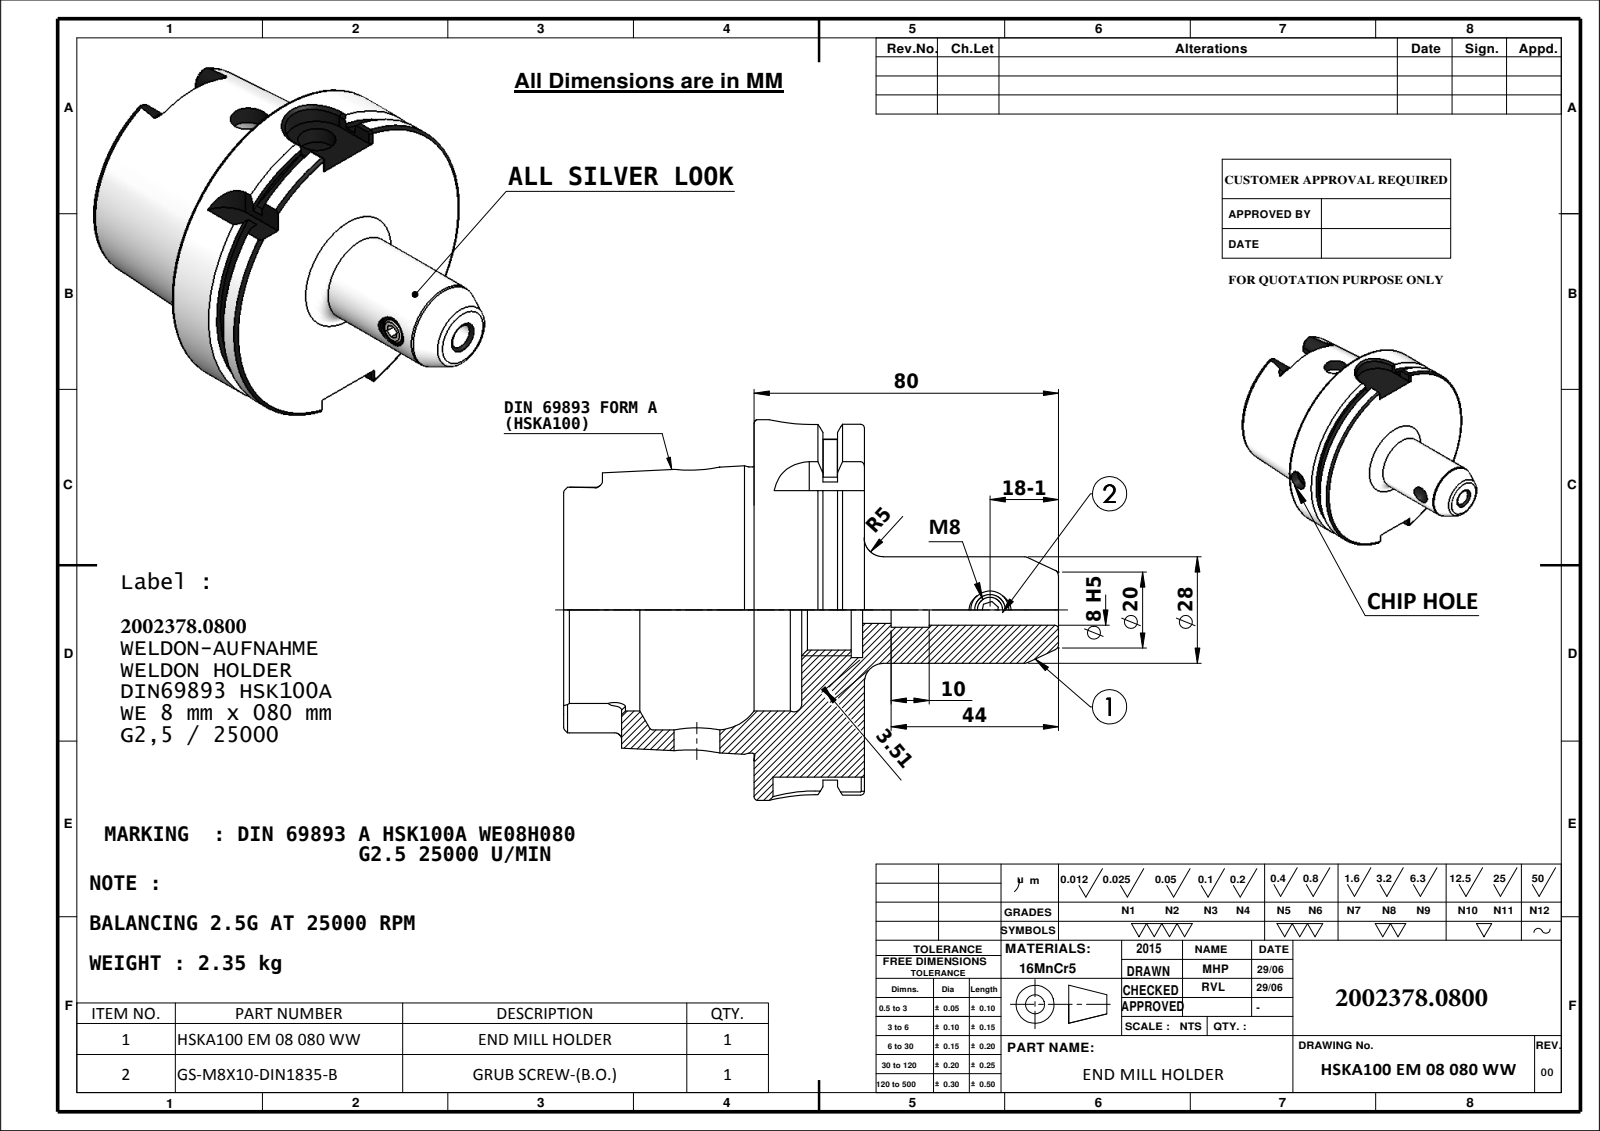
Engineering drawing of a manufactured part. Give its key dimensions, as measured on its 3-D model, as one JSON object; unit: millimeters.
{"part_name": "91100A-WE8 08080; M8X10._DIN 913 - M8 x 8-N; HSKA100 EM 08 080 WW", "step_written_by": "SolidWorks 2009 (CONFIG_CONTROL_DESIGN)", "units": "millimeters", "bodies": {"solids": 2, "faces": 204, "planar": 64, "cylindrical": 58, "other": 82}, "overall_size": [130, 100, 100], "volume_mm3": 281771, "surface_area_mm2": 55679, "round_holes": [[10, 2], [12, 2], [6.8, 1], [7, 1], [8, 1], [9, 1], [21, 1], [25, 1], [53, 1], [63, 1]], "round_bosses_or_shafts": [[100, 1], [92, 1], [75.16, 1], [28, 1], [8, 1]], "partial_cylinders_radius": [[1.8, 6], [4.88, 4], [10, 2], [11, 1]], "face_to_face_distances": [29, 12.5, 16.5, 50, 62.5, 79, 78.5, 28.5, 16, 0.5], "hole_center_spacings": [30, 55]}
